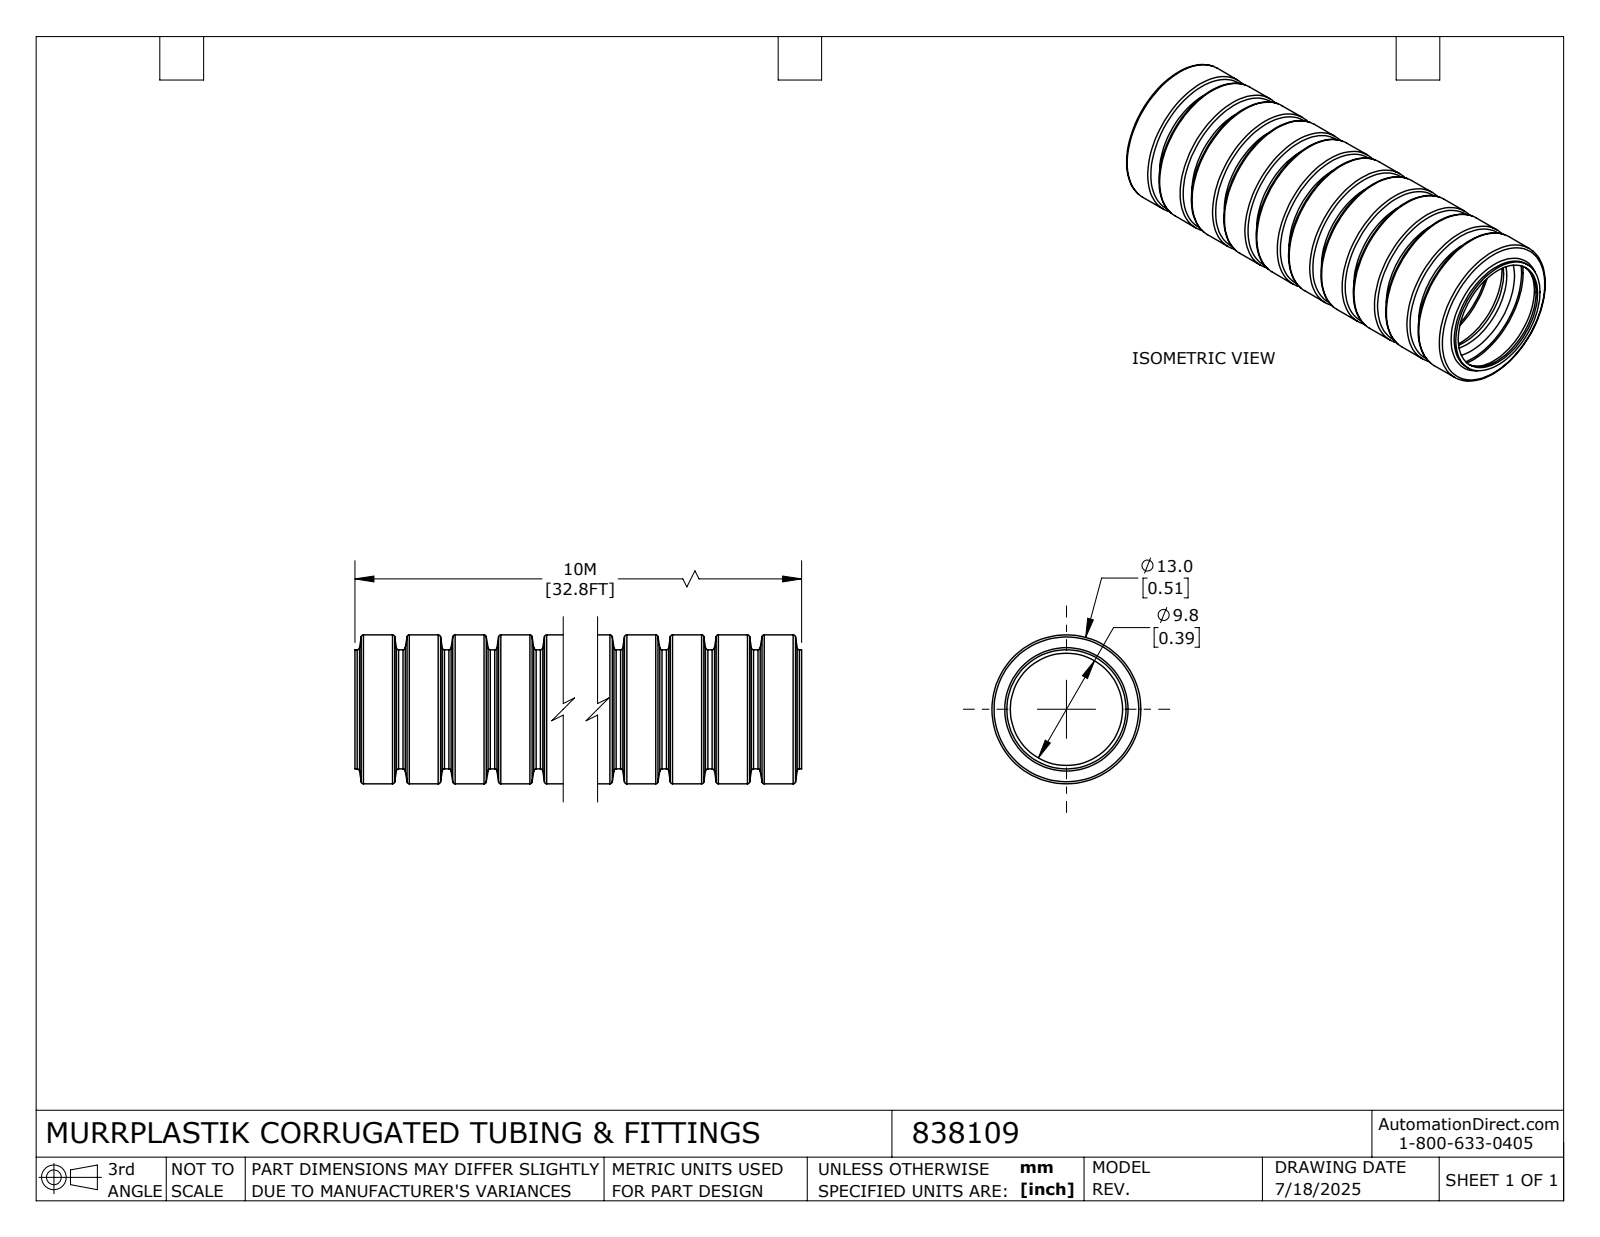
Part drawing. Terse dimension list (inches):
name: 838109_Default
written by: SolidWorks 2024 (CONFIG_CONTROL_DESIGN)
unit: in
bodies: 1 solid, 164 faces (2 planar, 42 cylindrical, 120 other)
size: 1.575 × 0.512 × 0.512
volume: 0.041 in³; area: 6.834 in²
holes: 1× ⌀0.386, 1× ⌀0.488
bosses: 1× ⌀0.512, 1× ⌀0.409
face distances: 1.575
